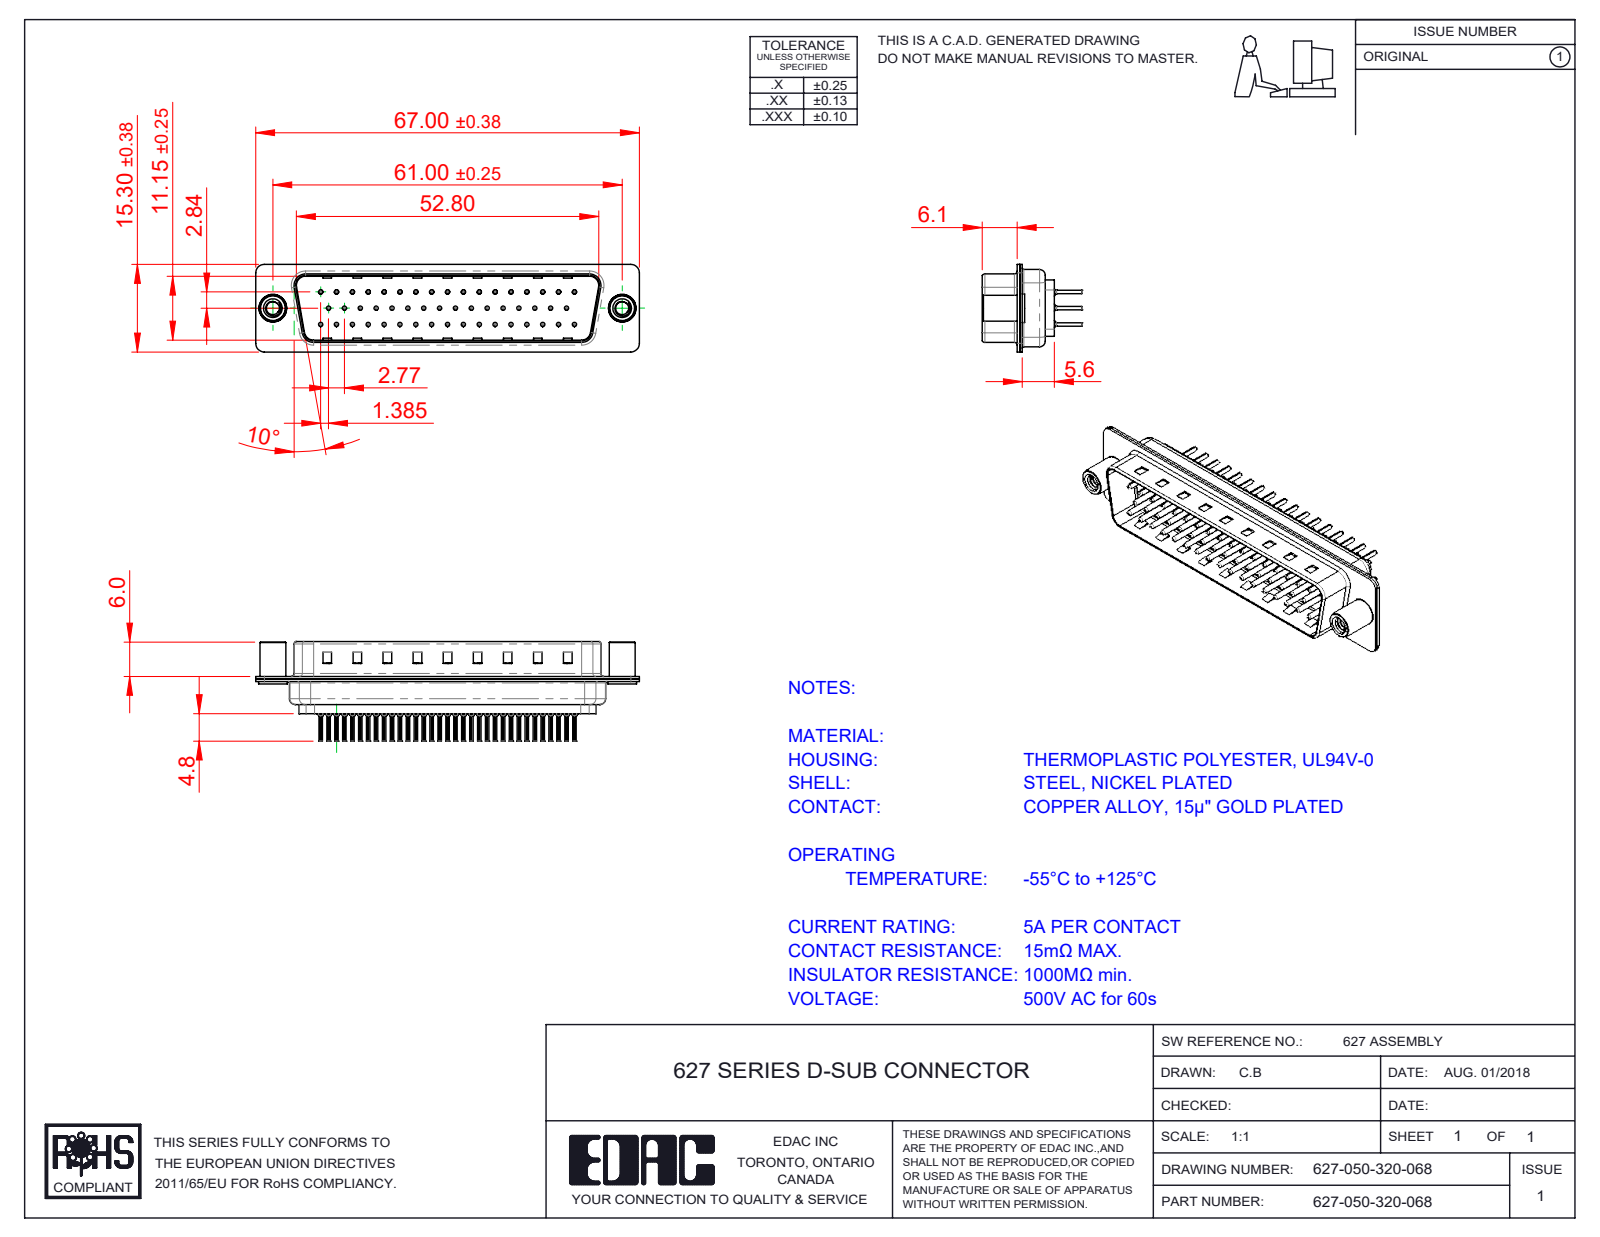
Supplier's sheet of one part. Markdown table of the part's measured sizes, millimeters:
| quantity | value |
| --- | --- |
| part name | 627 Contact Row 1_20L; 627 Contact Row 2_20L; 627 4-40 Threaded Standoff; 627 Contact Row 3_20L (+4 more) |
| STEP written by | SolidWorks 2020 (CONFIG_CONTROL_DESIGN) |
| units | millimeters |
| bodies | 55 solids, 5346 faces (1405 planar, 2019 cylindrical, 1922 other) |
| overall size | 67 × 17.3 × 15.3 |
| volume | 4 487 mm³ |
| surface area | 12 779 mm² |
| round holes (diameter × count) | 0.2 × 50, 0.35 × 50, 1.1 × 50, 1.6 × 50, 2.26 × 2, 4 × 2, 4.8 × 2 |
| round bosses / shafts (diameter × count) | 2 × 50, 1.5 × 50, 0.75 × 50, 0.6 × 50, 5 × 2, 4.9 × 2, 4.5 × 2 |
| partial cylindrical surfaces (radius × count) | 0.1 × 100, 1.5 × 16, 2 × 12, 0.5 × 8, 1.6 × 8, 0.25 × 4, 0.6 × 4, 0.65 × 4 |
| main face-to-face distances | 0.4, 0.45, 11.55, 0.9, 6.05, 6.5, 0.78, 12.33, 1.95, 0.77 |
| hole center spacings | 3.16, 2.77, 5.54, 8.31, 11.08, 13.85, 16.62, 5.03 |
